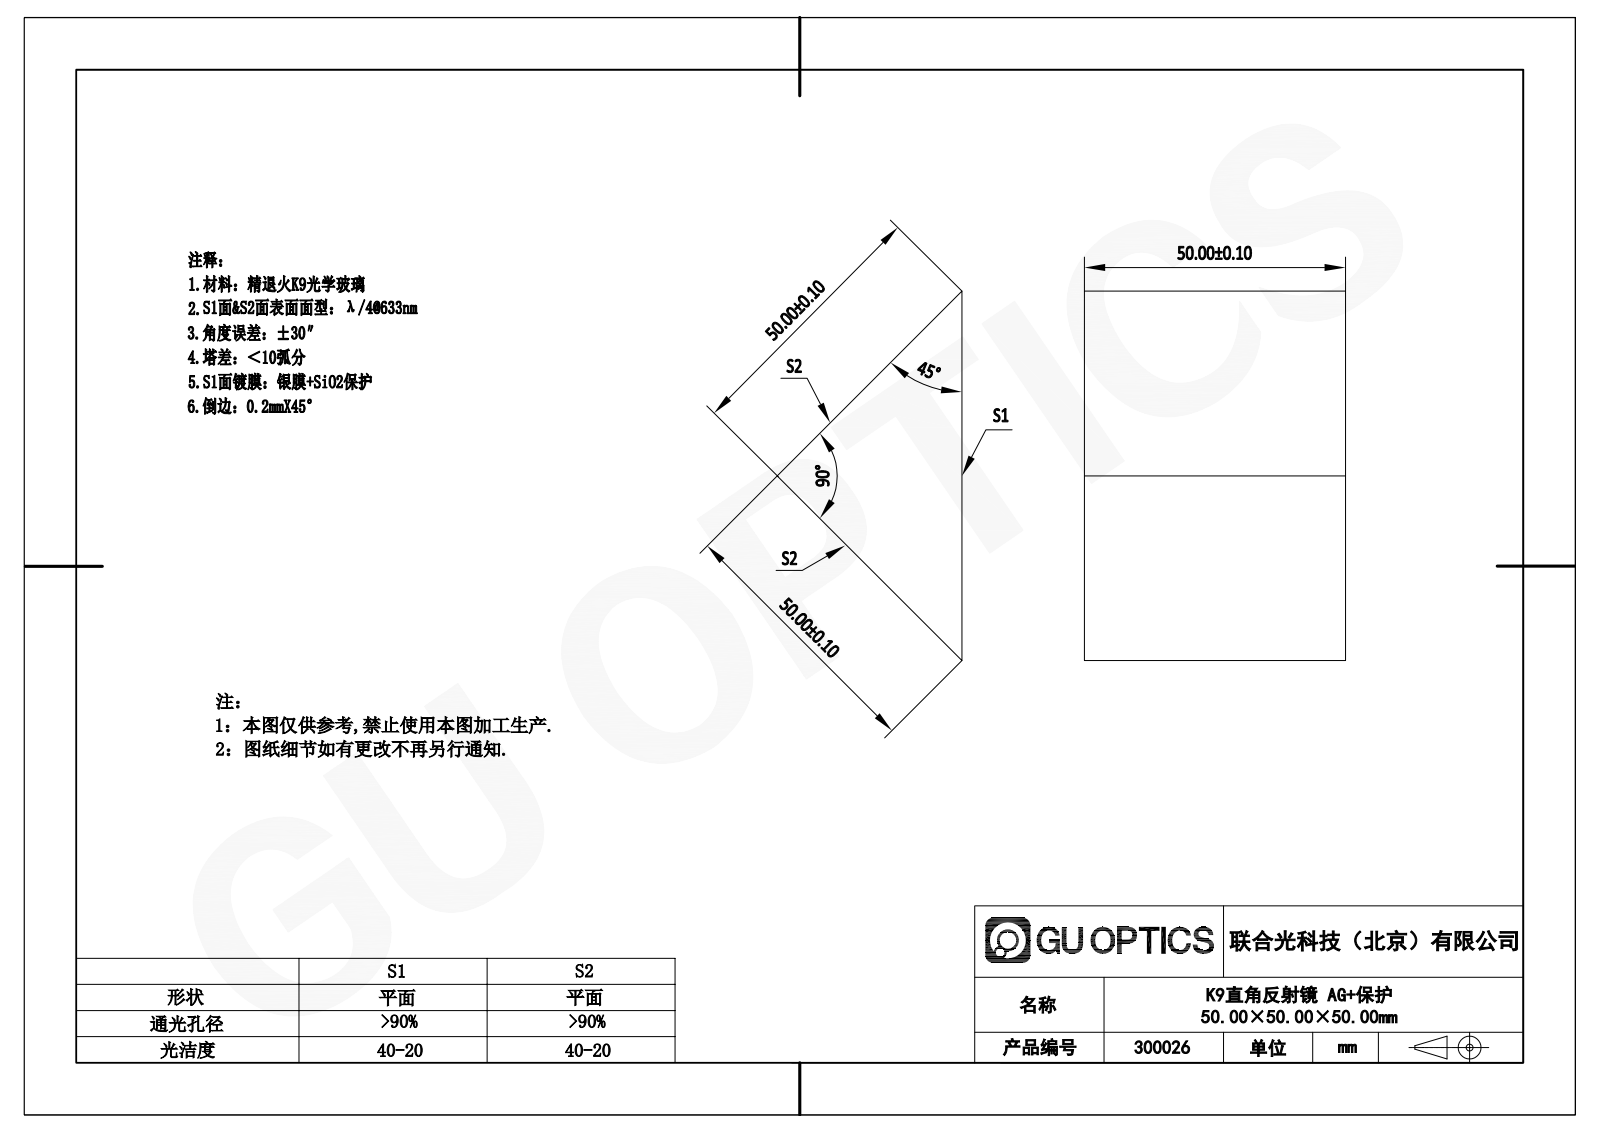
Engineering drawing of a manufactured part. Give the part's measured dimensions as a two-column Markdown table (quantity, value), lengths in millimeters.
| quantity | value |
| --- | --- |
| part name | 300008 |
| STEP written by | SolidWorks 2016 (AUTOMOTIVE_DESIGN) |
| units | millimeters |
| bodies | 1 solid, 5 faces (5 planar, 0 cylindrical, 0 other) |
| overall size | 70.71 × 50 × 35.35 |
| volume | 62 500 mm³ |
| surface area | 11 036 mm² |
| main face-to-face distances | 50 |
